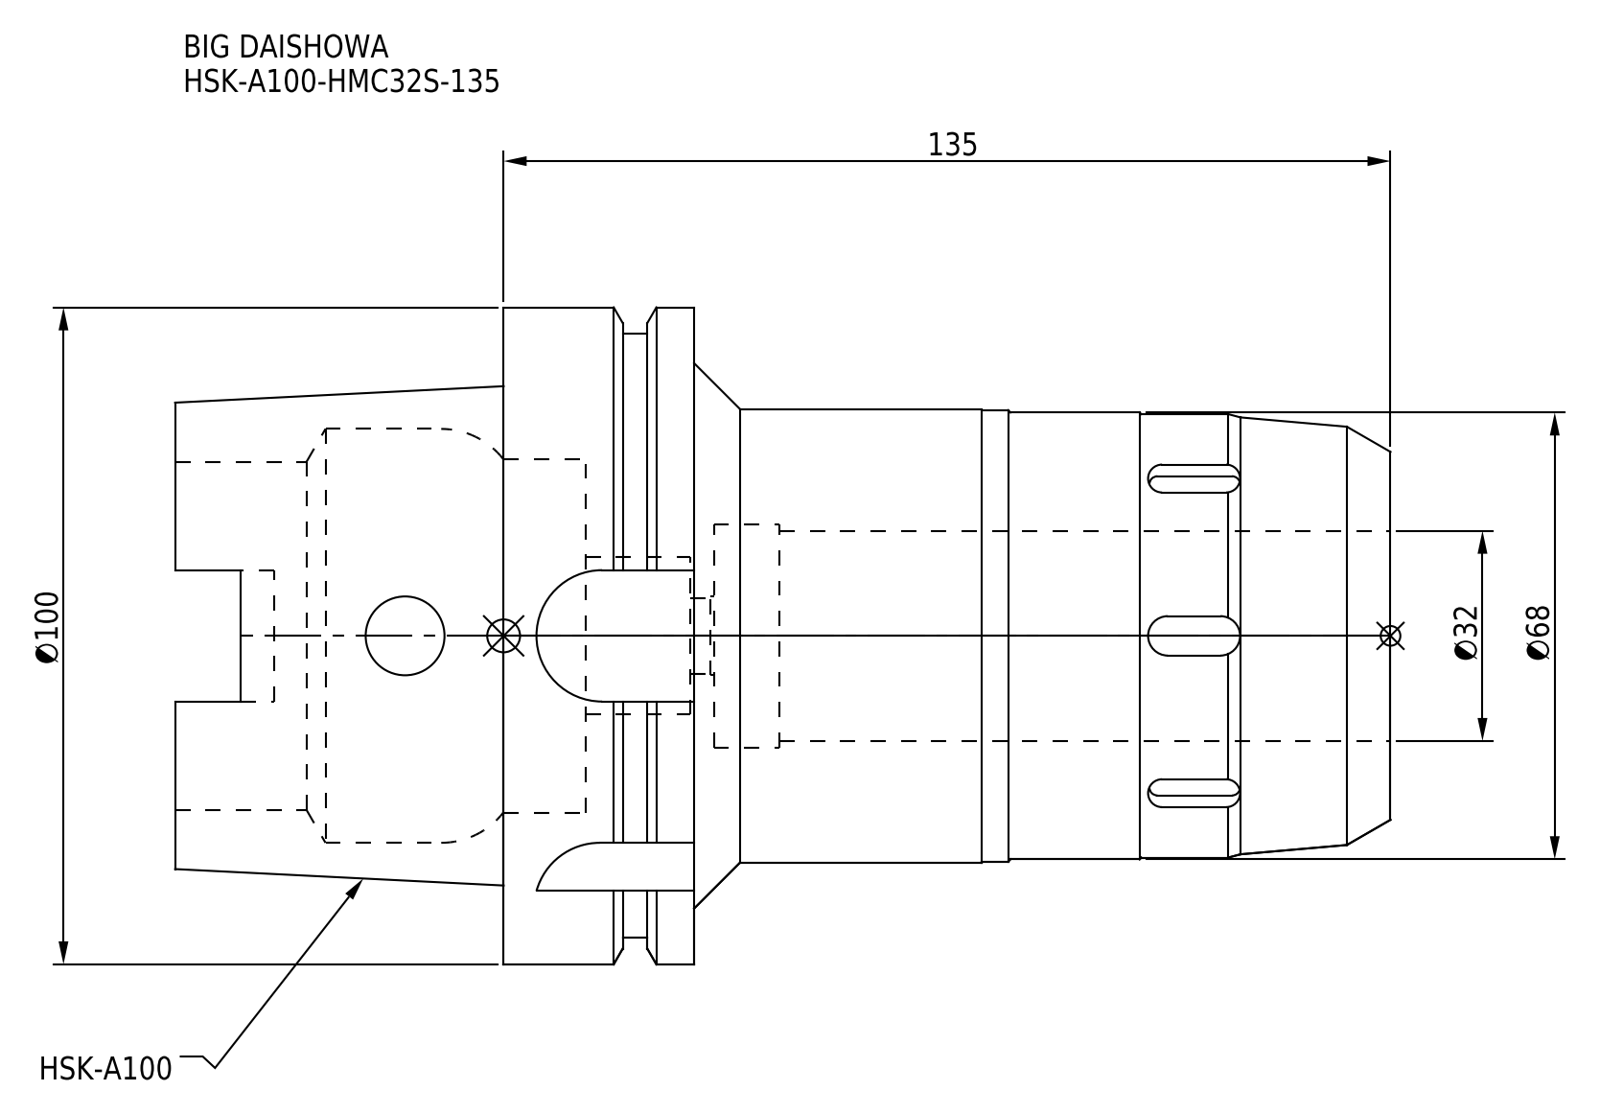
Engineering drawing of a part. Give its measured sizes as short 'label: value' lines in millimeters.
name: HSK-A100-HMC32S-135
written by: CREO PARAMETRIC BY PTC INC, 2016380 (AUTOMOTIVE_DESIGN)
unit: mm
bodies: 1 solid, 146 faces (60 planar, 62 cylindrical, 24 other)
size: 185 × 100 × 100
volume: 552 433 mm³; area: 81 898 mm²
holes: 2× ⌀12, 1× ⌀11.5, 1× ⌀24, 1× ⌀32, 1× ⌀34, 1× ⌀53, 1× ⌀53.8, 1× ⌀63
bosses: 1× ⌀100, 1× ⌀92, 1× ⌀69, 1× ⌀68.7, 1× ⌀68, 1× ⌀67.5
rounds: 12× R3, 4× R4.88, 4× R10
face distances: 29, 16.55, 12.45, 106, 122.55, 135, 185, 79, 62.45, 50
